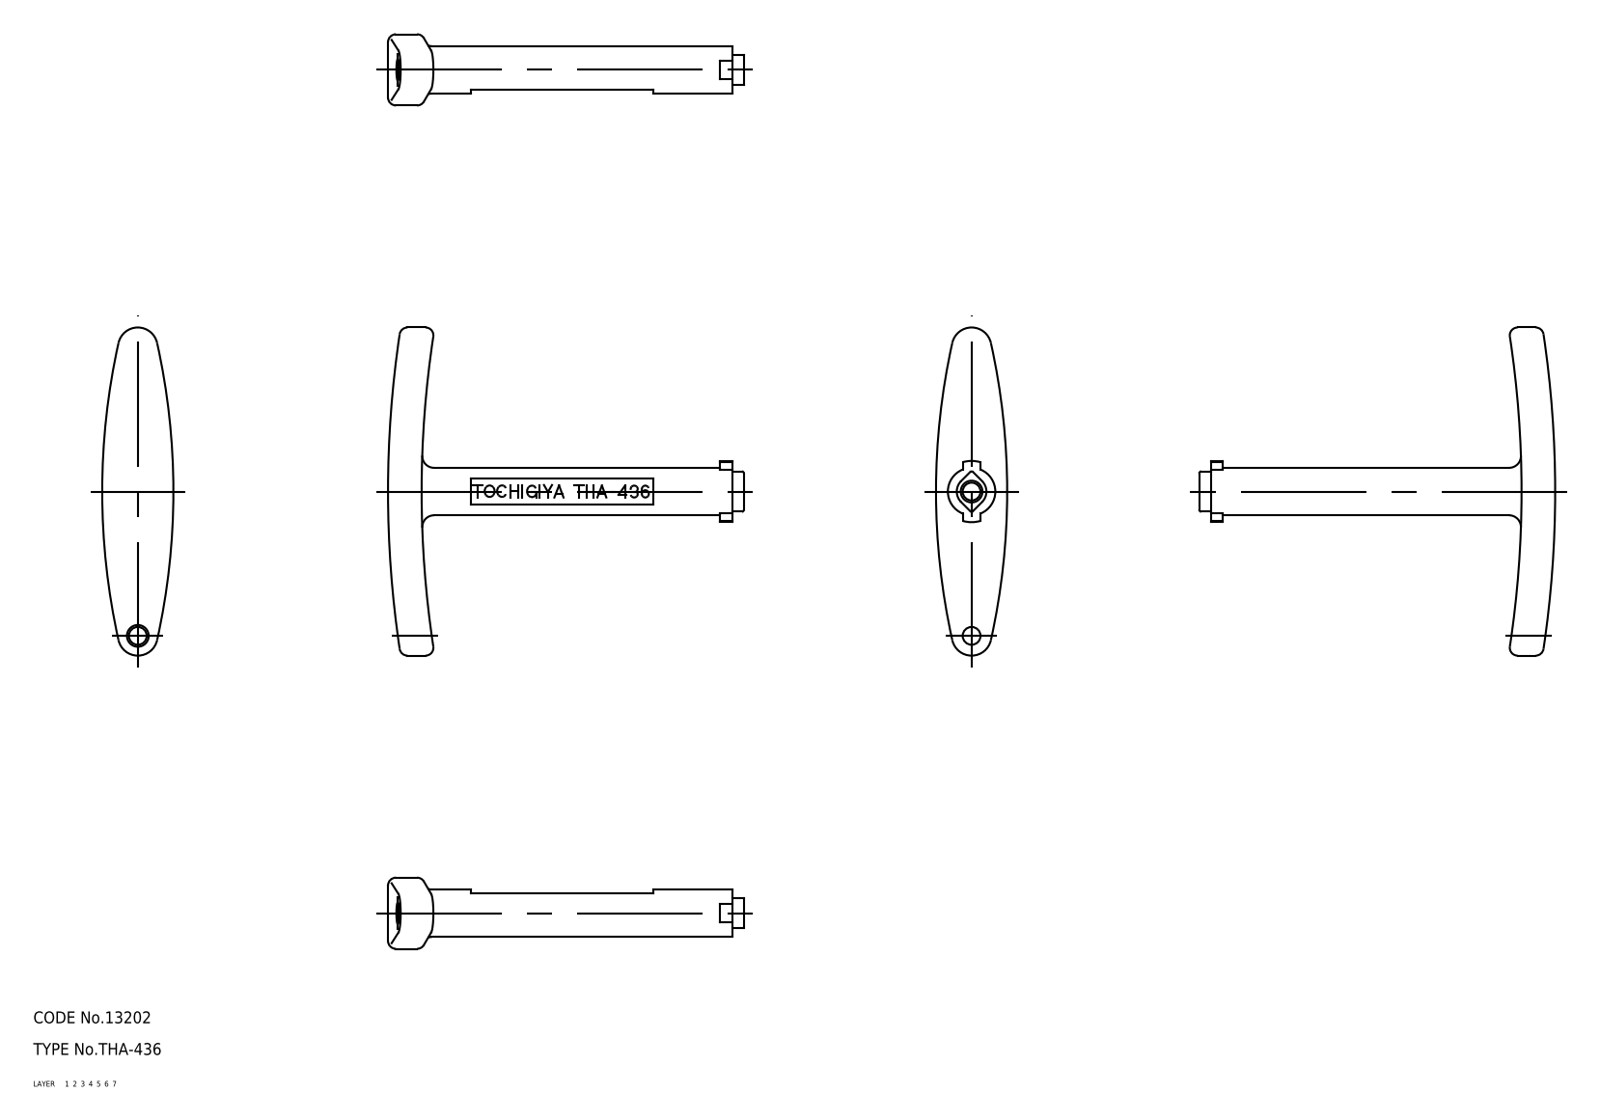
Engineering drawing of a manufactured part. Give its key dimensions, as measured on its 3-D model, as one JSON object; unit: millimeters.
{"part_name": "key_handle", "step_written_by": "CADfix (AUTOMOTIVE_DESIGN)", "units": "millimeters", "bodies": {"solids": 1, "faces": 47, "planar": 0, "cylindrical": 0, "other": 47}, "overall_size": [90, 83, 18], "volume_mm3": 18600, "surface_area_mm2": 6898}
